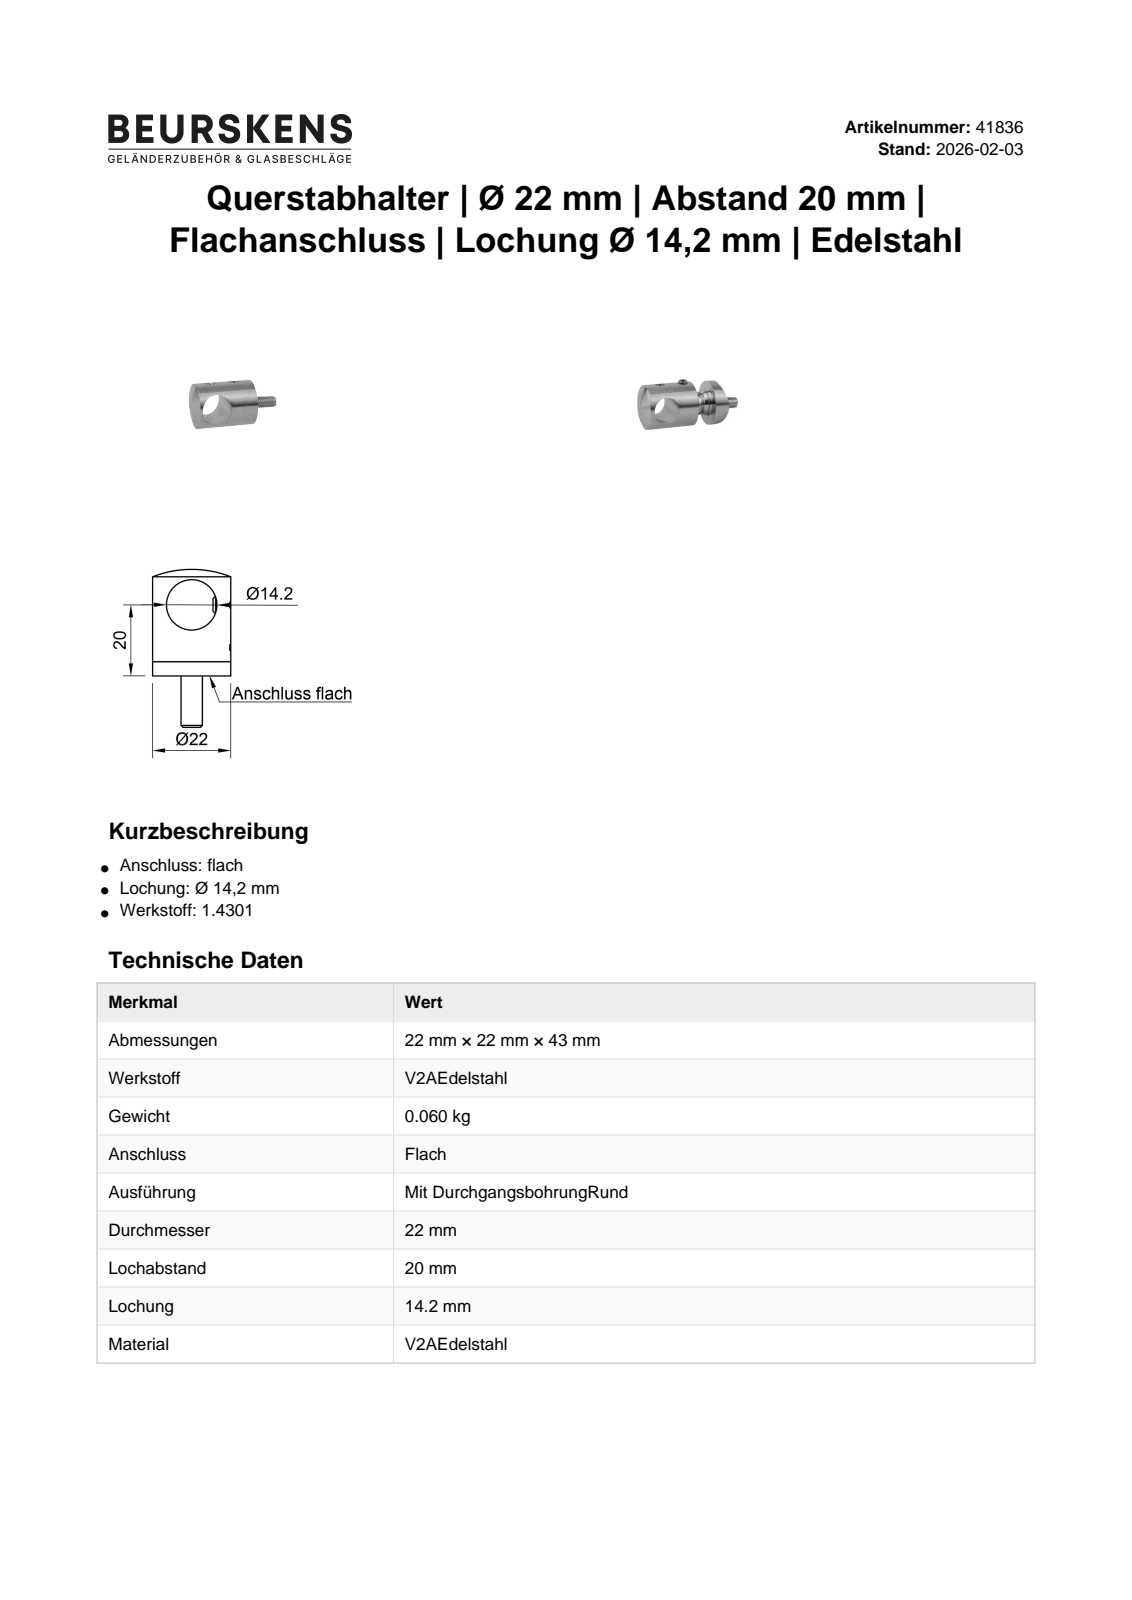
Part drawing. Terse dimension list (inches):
name: 41836 for customer; socket set screw flat point_din_DIN 913 - M5 x 5-N; socket countersunk head screw_din_DIN 7991 - M6 x 25 --- 18.7N; H-22-42.4ñ
written by: SolidWorks 2020 (CONFIG_CONTROL_DESIGN)
unit: in
bodies: 5 solids, 95 faces (39 planar, 26 cylindrical, 30 other)
size: 1.751 × 0.866 × 0.866
volume: 0.471 in³; area: 8.634 in²
holes: 2× ⌀0.157, 1× ⌀0.276, 1× ⌀0.441, 1× ⌀0.551, 1× ⌀0.559
bosses: 2× ⌀0.197, 1× ⌀0.866, 1× ⌀0.504, 1× ⌀0.456, 1× ⌀0.236
face distances: 0.157, 0.079, 0.414, 0.256, 0.335, 0.374, 0.531, 0.453, 0.118, 0.236
hole spacings: 0.472
